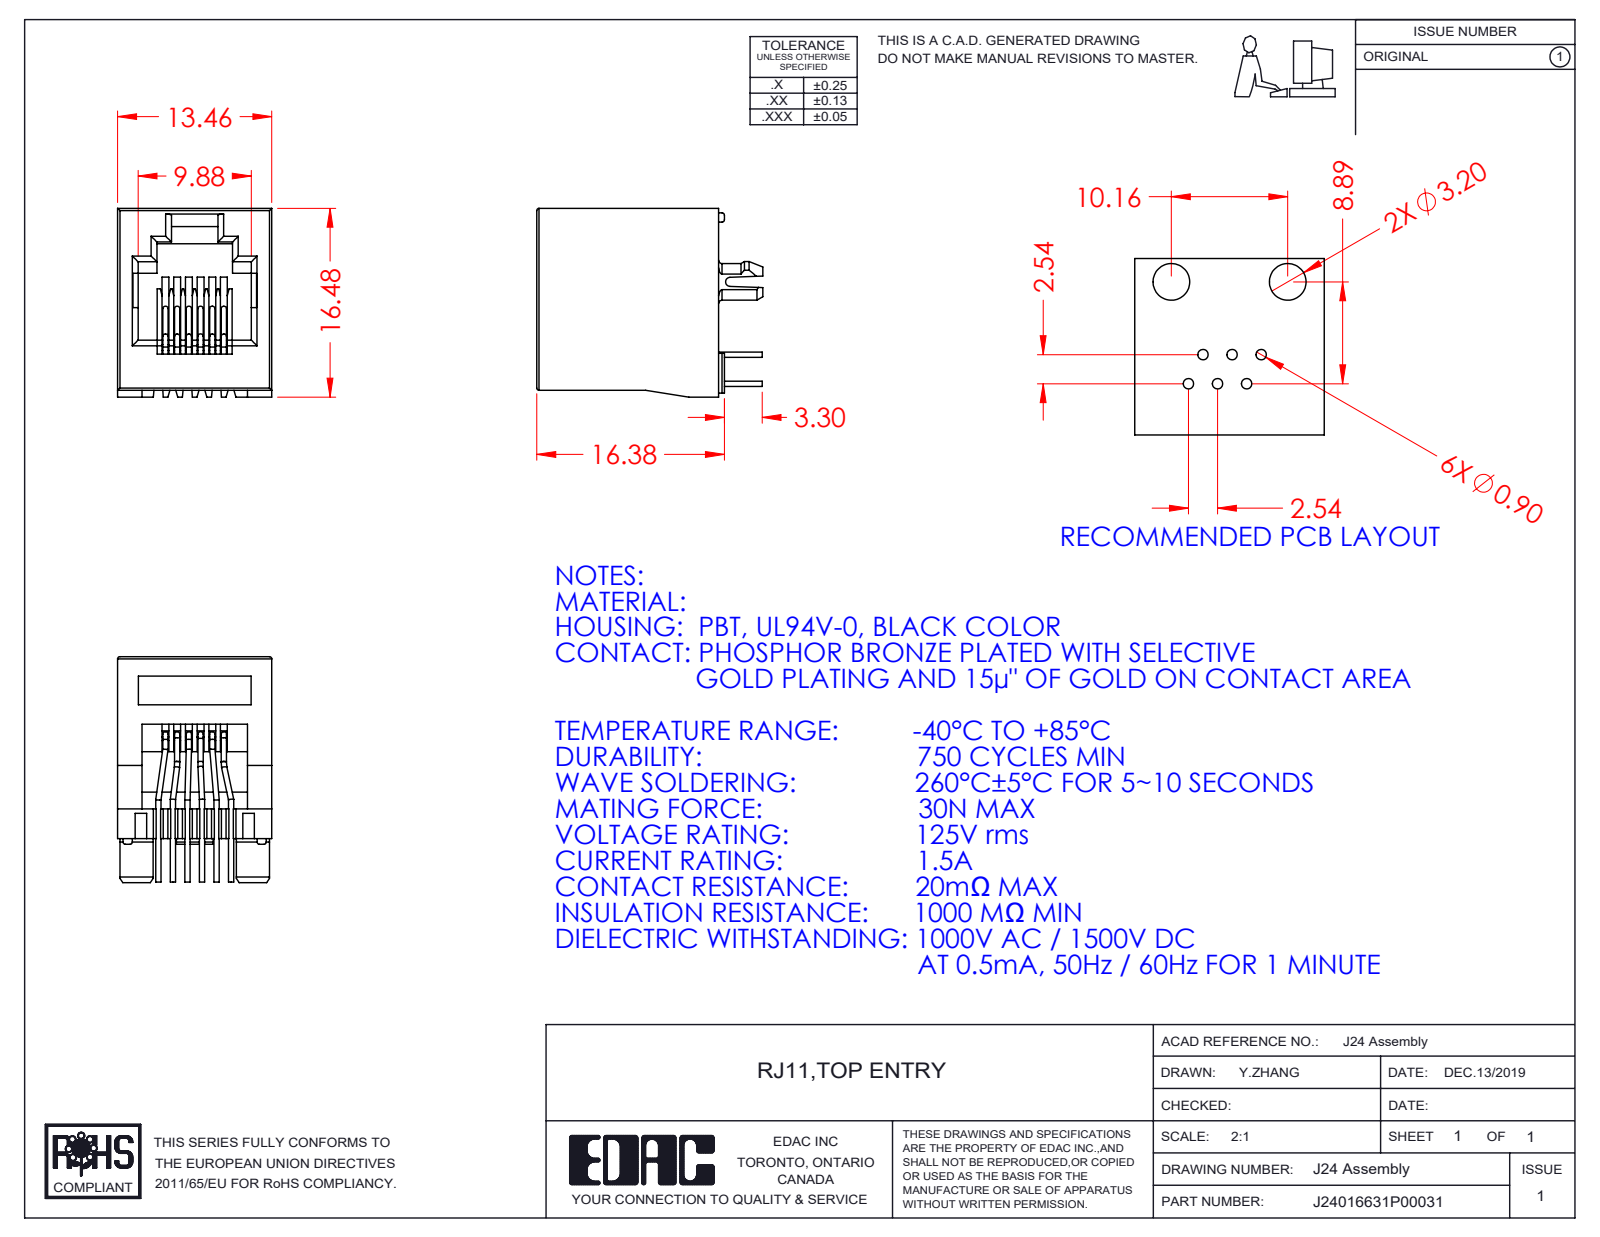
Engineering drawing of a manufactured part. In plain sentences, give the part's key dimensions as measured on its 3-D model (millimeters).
The part is named "24 Insulator_Standard; 24 Contacts_Standard; RJ24016631P00031". Its 3-D file was written by "SolidWorks 2016 (CONFIG_CONTROL_DESIGN)". It is 7 solids with 444 faces: 256 planar, 150 cylindrical and 38 other. Overall it measures 19.73 by 16.48 by 13.46 millimeters. Its volume is 1 745 cubic millimeters and its surface area 2 930 square millimeters. Round holes: 6 of diameter 0.46, 2 of diameter 2.1. Round bosses or shafts: 26 of diameter 0.46. Partial cylindrical surfaces (rounded edges, fillets, slot ends): 16 of radius 0.5, 10 of radius 0.2, 6 of radius 0.32, 6 of radius 0.34, 3 of radius 0.25, 2 of radius 1.6, 2 of radius 1.77, 1 of radius 0.4. The main face-to-face distances are 13.46, 1.02, 1.79, 11.67, 0.6, 15.87, 8.24, 3.43, 10.03, 1.64. The hole center spacings are 2.84, 2.54, 4.58, 5.08, 13.1, 6.84, 10.16, 10.35.
